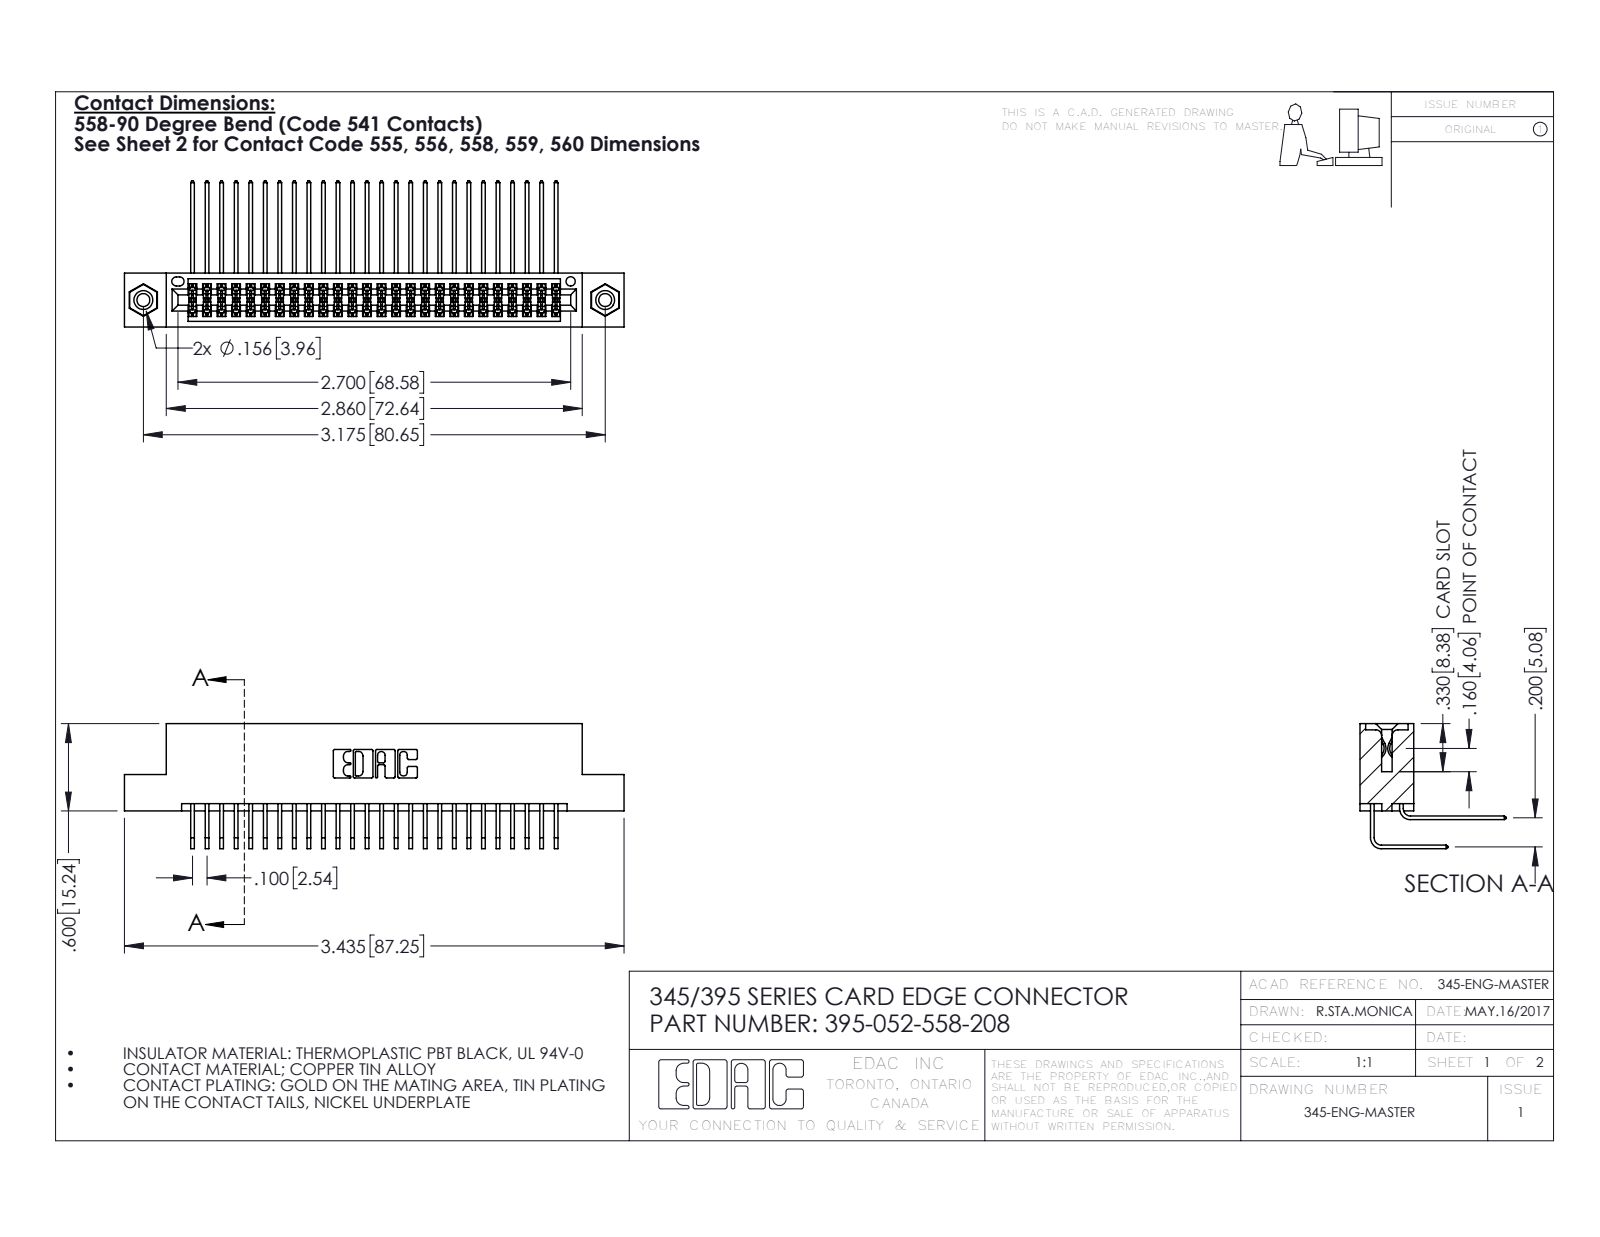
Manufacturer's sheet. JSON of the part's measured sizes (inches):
{"part_name": "345-292-001_558 Tail - 2; 395-052-558-208; 345-292-001_558 559 Tail - 1; 345 Part_Flush Mounting Lugs - 0.156 Dia-TI (+1 more)", "step_written_by": "SolidWorks 2016 (CONFIG_CONTROL_DESIGN)", "units": "inches", "bodies": {"solids": 55, "faces": 2890, "planar": 1932, "cylindrical": 942, "other": 16}, "overall_size": [3.435, 1.005, 0.859], "volume_in3": 0.526, "surface_area_in2": 21.48, "round_holes": [[0.089, 2], [0.125, 2], [0.156, 2], [0.064, 1]], "round_bosses_or_shafts": [[0.155, 2]], "partial_cylinders_radius": [[0.006, 79], [0.01, 22], [0.007, 6], [0.031, 6], [0.026, 3], [0.014, 2], [0.019, 2], [0.022, 2]], "face_to_face_distances": [0.2, 0.072, 0.298, 0.37, 0.098, 0.272, 0.025, 0.225, 0.025, 0.285], "hole_center_spacings": [0.27, 2.94, 3.175]}
